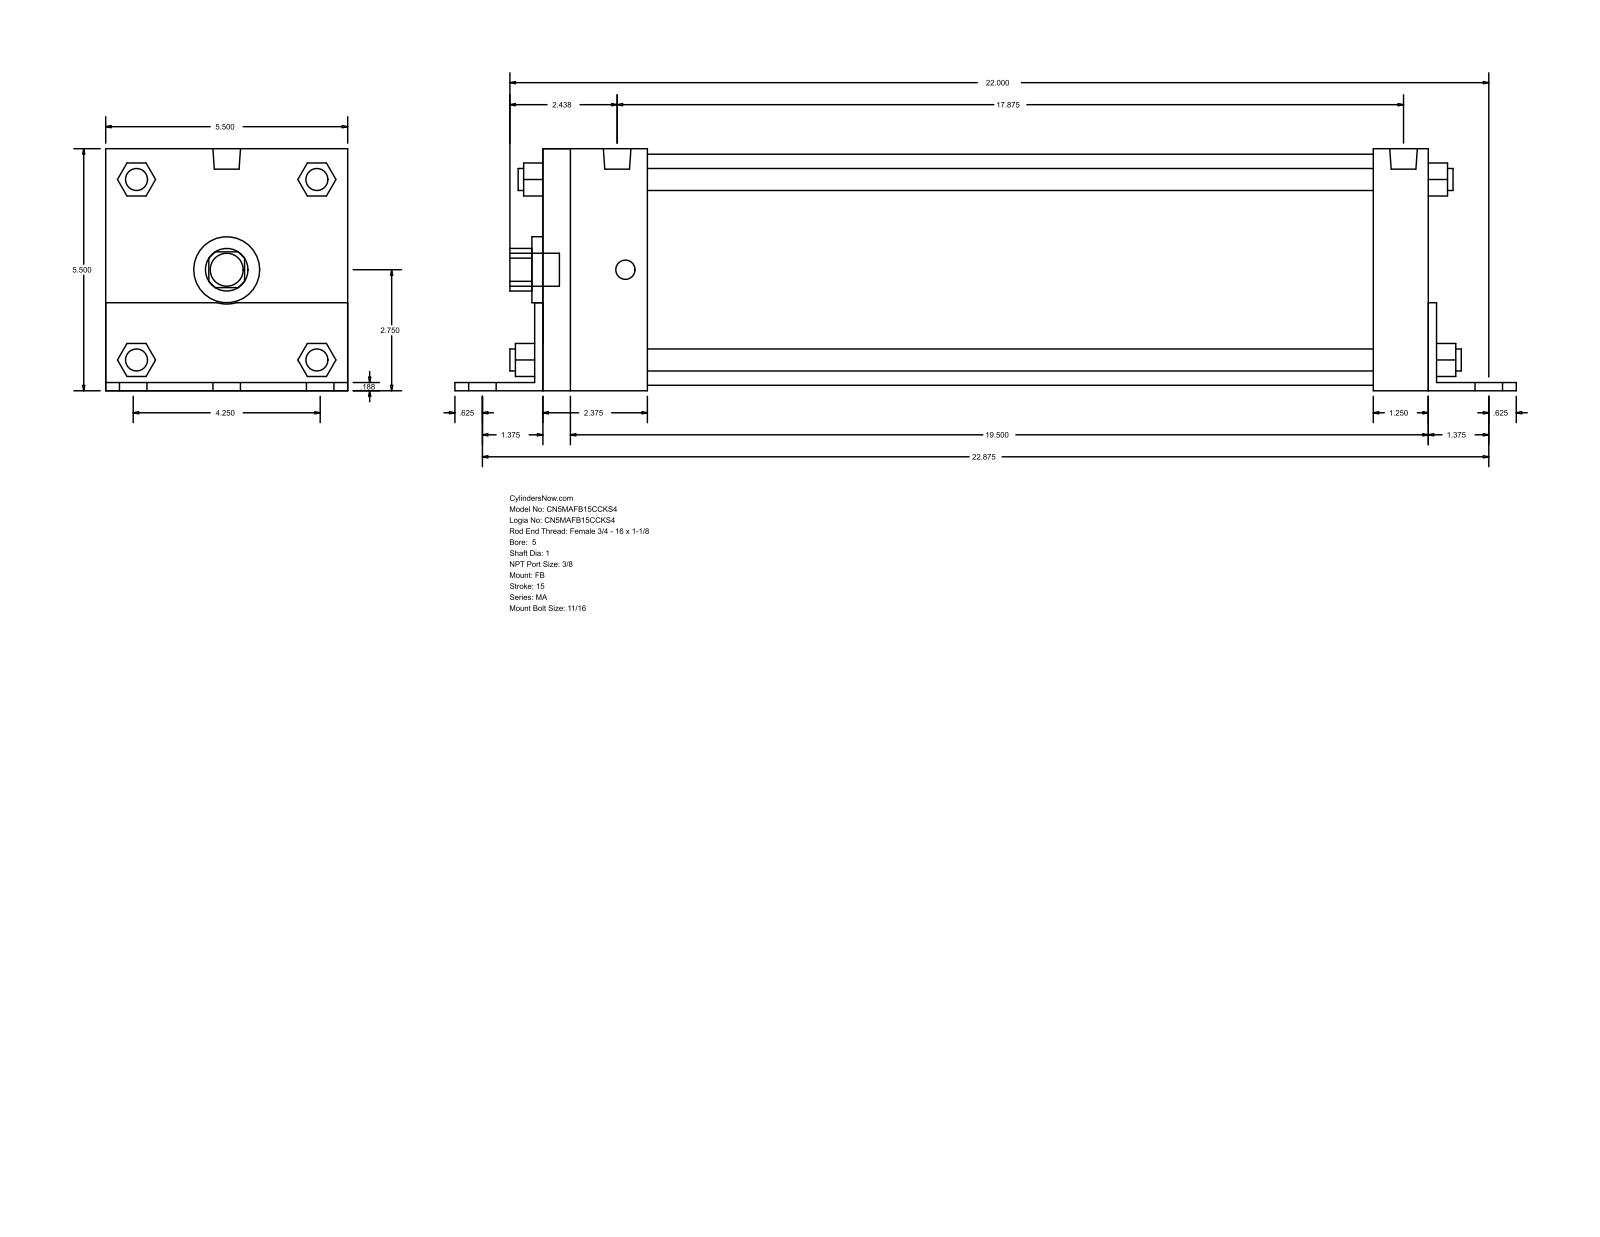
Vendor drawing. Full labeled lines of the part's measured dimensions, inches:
Part name (STEP PRODUCT): MA_FB__0500_1
STEP written by: GSSL Pune (CONFIG_CONTROL_DESIGN)
Units: inches
Bodies: 0 solids, 140 faces (105 planar, 35 cylindrical, 0 other)
Overall size (bounding box): 24.125 × 5.502 × 5.5
Round holes (diameter × count): ⌀1 ×1, ⌀1.5 ×1, ⌀5.25 ×1
Round bosses / shafts (diameter × count): ⌀0.687 ×6, ⌀0.5 ×4, ⌀0.437 ×4, ⌀0.627 ×2, ⌀0.75 ×1
Partial cylindrical surfaces — rounded edges, fillets, slot ends (radius × count): R0.484 ×1, R0.78 ×1
Main face-to-face distances: 5.5, 0.187, 5.502, 20.313, 0.185, 5.315, 20.125, 20.5, 1.25, 1.437
